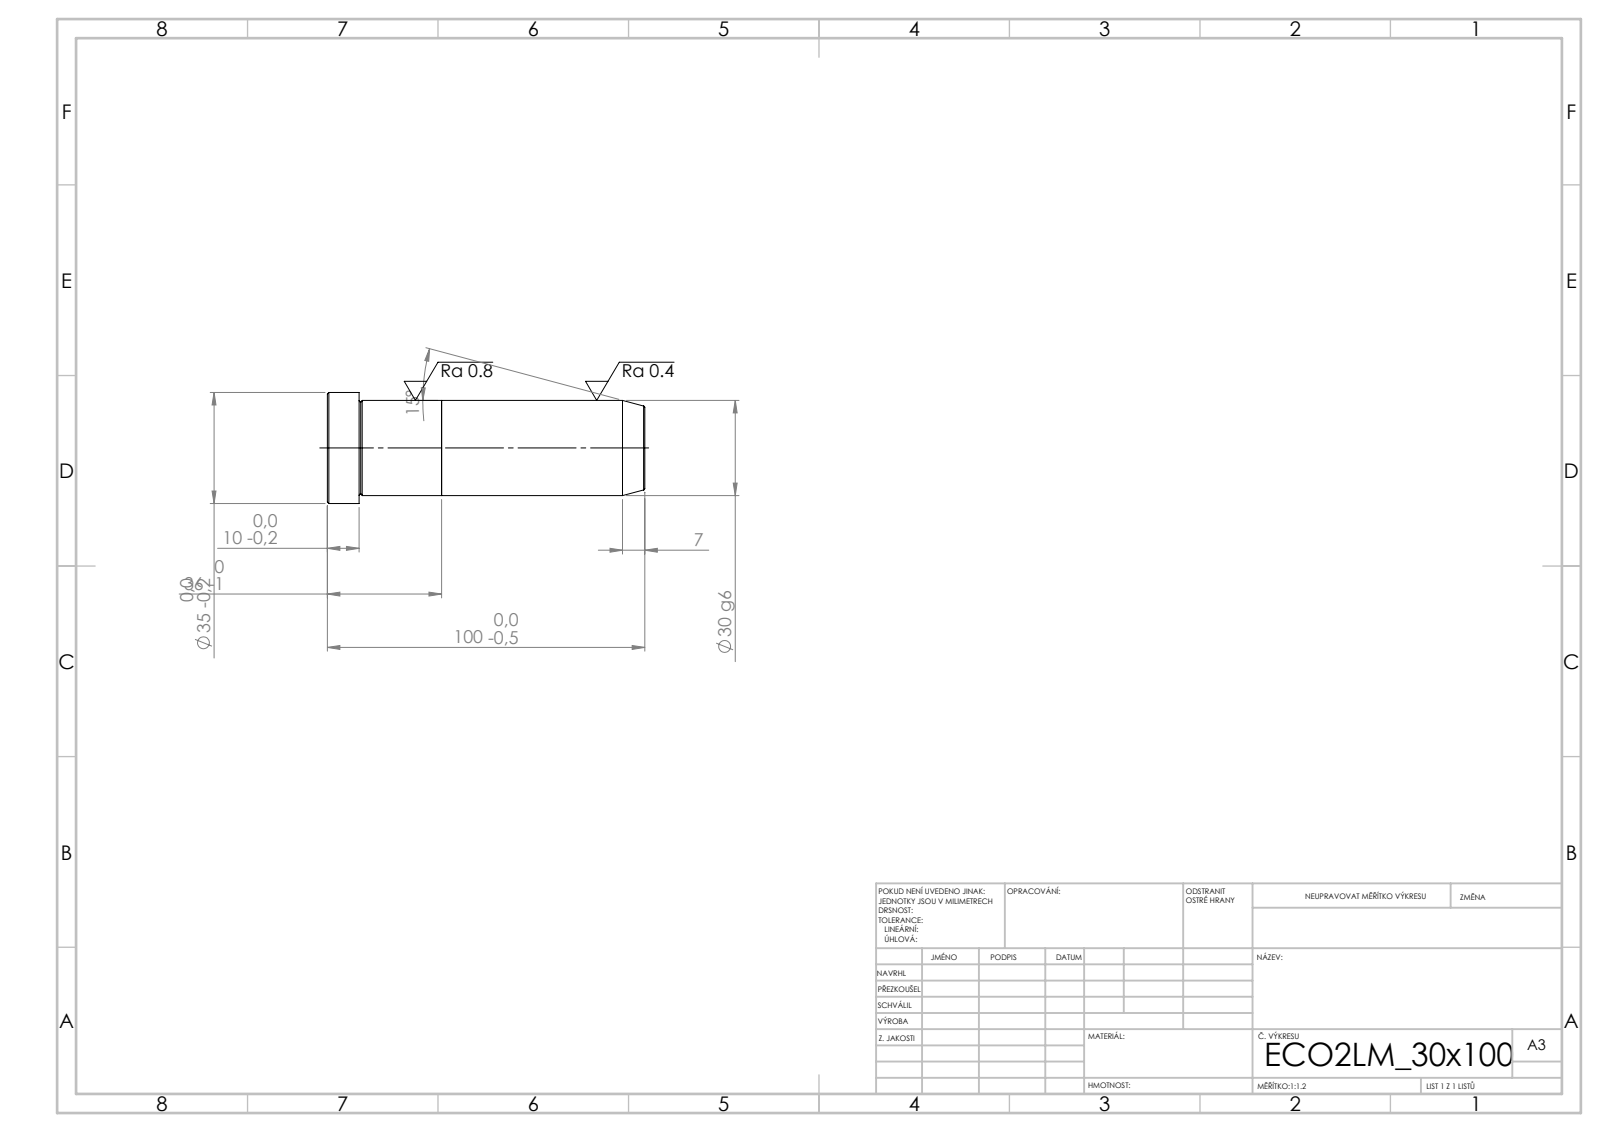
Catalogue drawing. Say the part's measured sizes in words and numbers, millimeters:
Its 3-D file was written by "SolidWorks 2019 (CONFIG_CONTROL_DESIGN)". It is 2 solids with 21 faces: 5 planar, 6 cylindrical and 10 other. Overall it measures 100 by 35 by 35 millimeters. Its volume is 72 593 cubic millimeters and its surface area 12 743 square millimeters. Round bosses or shafts: 1 of diameter 35, 1 of diameter 30. The main face-to-face distances are 36, 64, 100, 90, 26, 10.
